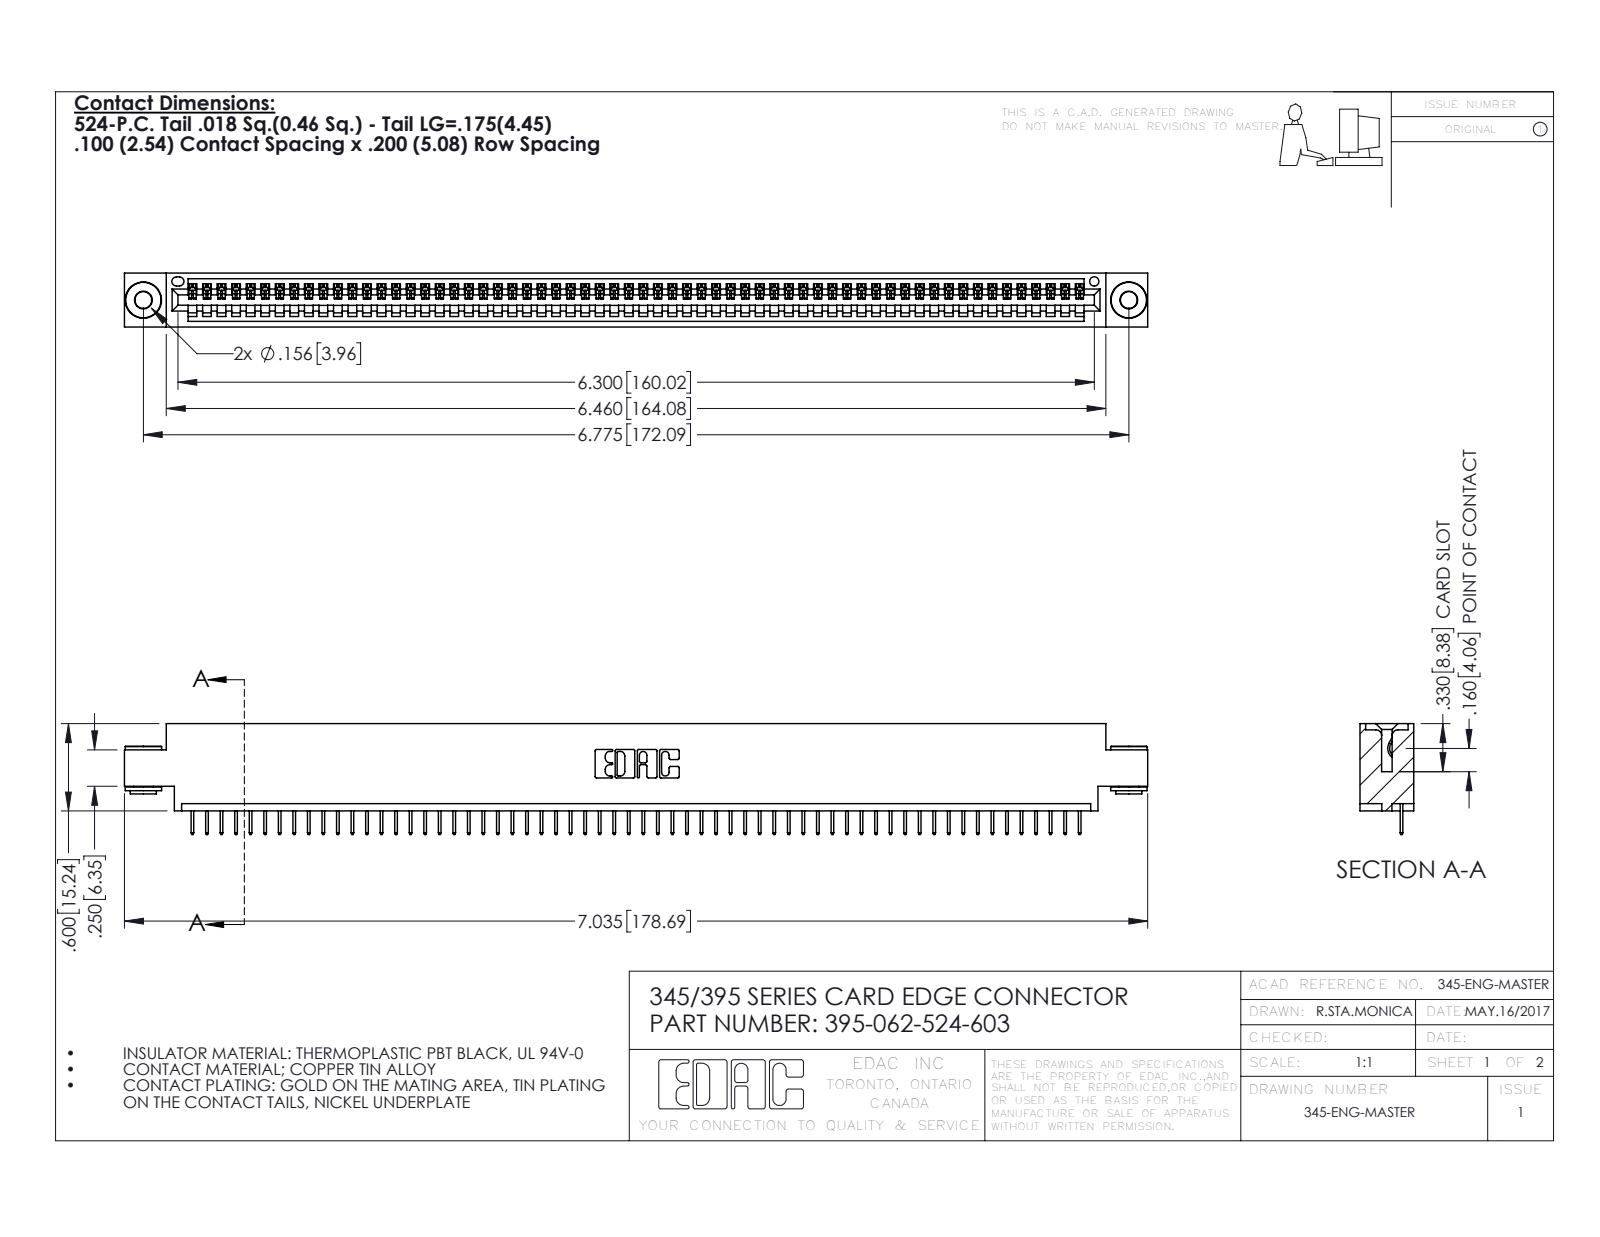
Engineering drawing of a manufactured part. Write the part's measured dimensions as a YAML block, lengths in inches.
part_name: "345-292-001_345-293-124; 345-250-002_345-250-002-102; 395-062-524-603; 345 Part_0.170 Offset - 0.156 Dia-TH"
step_written_by: "SolidWorks 2016 (CONFIG_CONTROL_DESIGN)"
units: inches
bodies: {solids: 65, faces: 4012, planar: 2946, cylindrical: 1058, other: 8}
overall_size: [7.035, 0.762, 0.37]
volume: 1.025
surface_area: 34.33
round_holes:
  - {diameter: 0.116, count: 2}
  - {diameter: 0.156, count: 2}
  - {diameter: 0.064, count: 1}
round_bosses_or_shafts:
  - {diameter: 0.25, count: 2}
  - {diameter: 0.18, count: 2}
  - {diameter: 0.136, count: 2}
partial_cylinders:
  - {radius: 0.006, count: 124}
  - {radius: 0.01, count: 22}
  - {radius: 0.007, count: 6}
  - {radius: 0.031, count: 6}
  - {radius: 0.026, count: 3}
  - {radius: 0.031, count: 2}
  - {radius: 0.04, count: 2}
  - {radius: 0.014, count: 1}
face_to_face_distances: [0.072, 0.298, 0.37, 0.2, 0.098, 0.272, 0.025, 0.225, 0.072, 0.175]
hole_center_spacings: [0.27, 6.539, 6.775]
